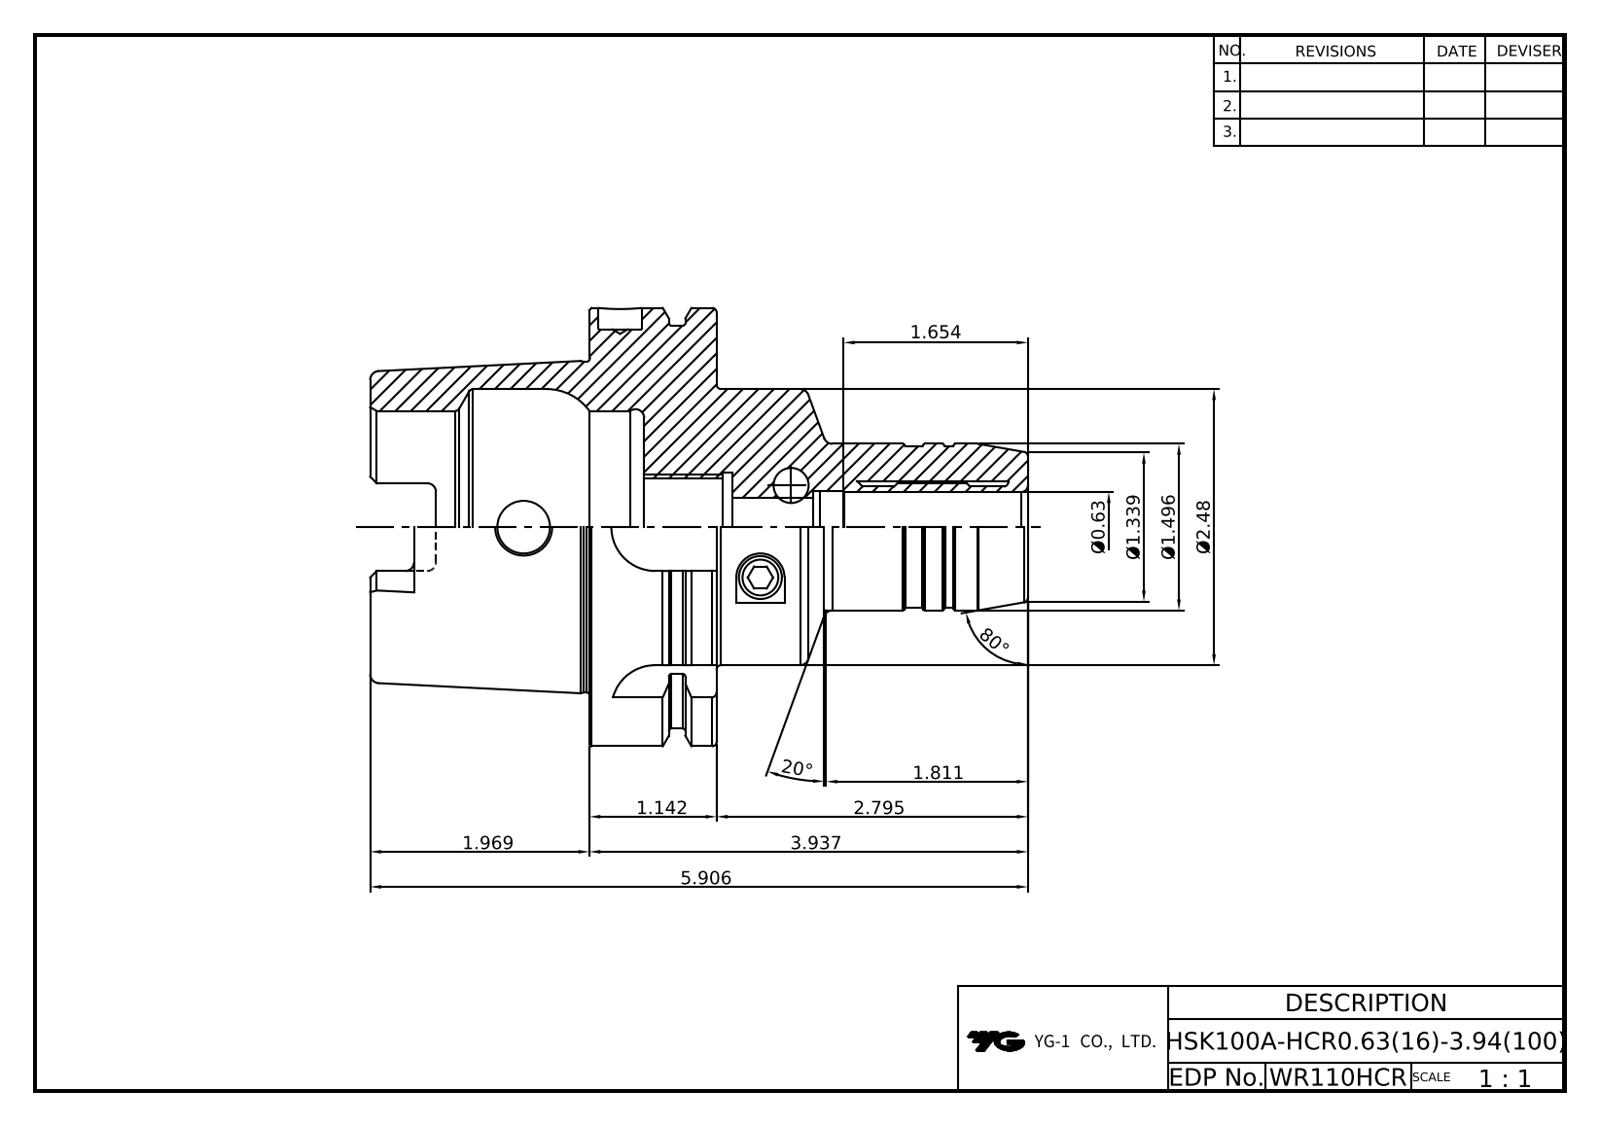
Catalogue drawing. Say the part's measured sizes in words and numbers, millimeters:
The part is named "LO-HSK100A-HCR16-100". Its 3-D file was written by "Autodesk Inventor 2025 (AUTOMOTIVE_DESIGN)". It is 1 solid with 134 faces: 38 planar, 39 cylindrical and 57 other. Overall it measures 150 by 100 by 100 millimeters. Its volume is 364 754 cubic millimeters and its surface area 62 088 square millimeters. Round holes: 1 of diameter 10, 1 of diameter 12, 1 of diameter 13.2, 1 of diameter 16, 1 of diameter 16.6, 1 of diameter 22.38, 1 of diameter 25, 1 of diameter 53, 1 of diameter 63. Round bosses or shafts: 1 of diameter 100, 1 of diameter 92, 1 of diameter 75.41, 1 of diameter 38, 1 of diameter 37. Partial cylindrical surfaces (rounded edges, fillets, slot ends): 6 of radius 2, 4 of radius 4.88, 4 of radius 10. The main face-to-face distances are 29, 12.5, 16.5, 62.5, 50, 79, 150, 100, 87.5, 71.
